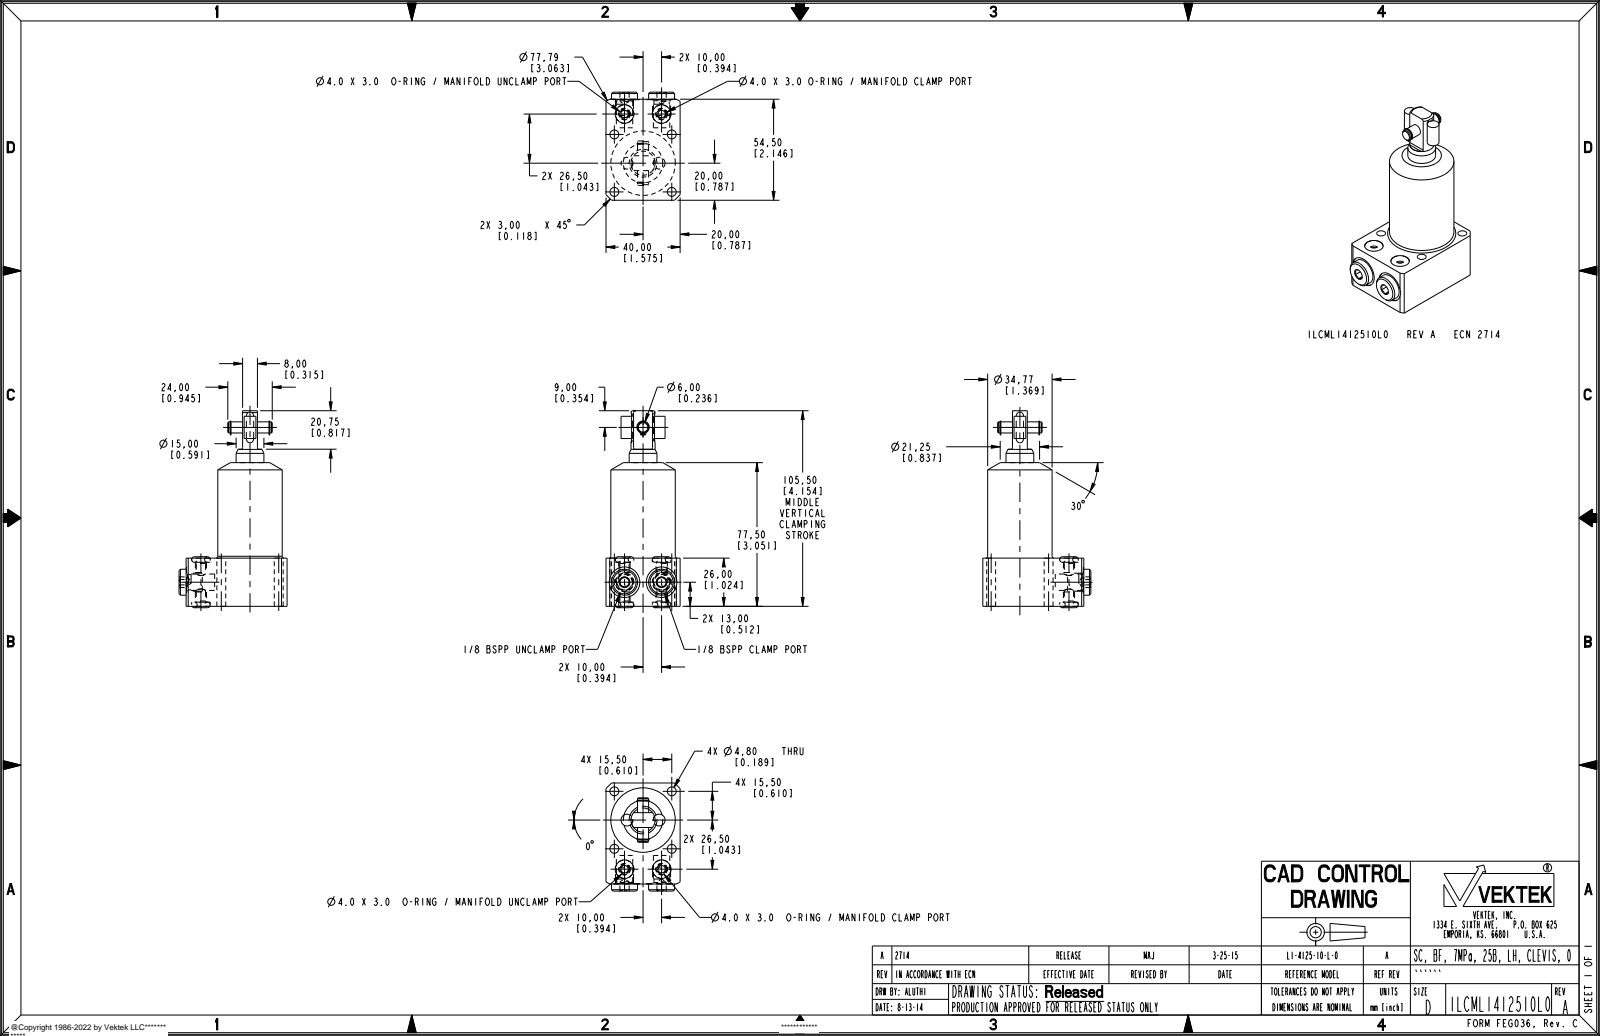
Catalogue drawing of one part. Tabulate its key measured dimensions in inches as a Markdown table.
| quantity | value |
| --- | --- |
| part name | ILCML1412510L0 |
| STEP written by | PRO/ENGINEER BY PARAMETRIC TECHNOLOGY CORPORATION, 2013320 (AUTOMOTIVE_DESIGN) |
| units | inches |
| bodies | 7 solids, 234 faces (80 planar, 98 cylindrical, 56 other) |
| overall size | 4.183 × 2.296 × 1.575 |
| volume | 6.42 in³ |
| surface area | 34.01 in² |
| round holes (diameter × count) | 0.189 × 4, 0.026 × 2, 0.197 × 2, 0.348 × 2, 0.394 × 2, 0.65 × 2 |
| round bosses / shafts (diameter × count) | 0.236 × 3, 0.551 × 2, 0.383 × 2, 0.325 × 2, 0.25 × 2, 1.369 × 1, 0.591 × 1, 0.512 × 1 |
| partial cylindrical surfaces (radius × count) | 0.026 × 2, 0.031 × 2, 0.042 × 2, 0.125 × 2, 1.531 × 1 |
| main face-to-face distances | 1.575, 1.024, 2.146, 0.63, 0.315, 0.945, 2.296, 0.15, 0.089, 0.935 |
| hole center spacings | 1.22, 0.484, 0.787, 1.093, 1.668, 1.726, 1.935, 3.171 |
